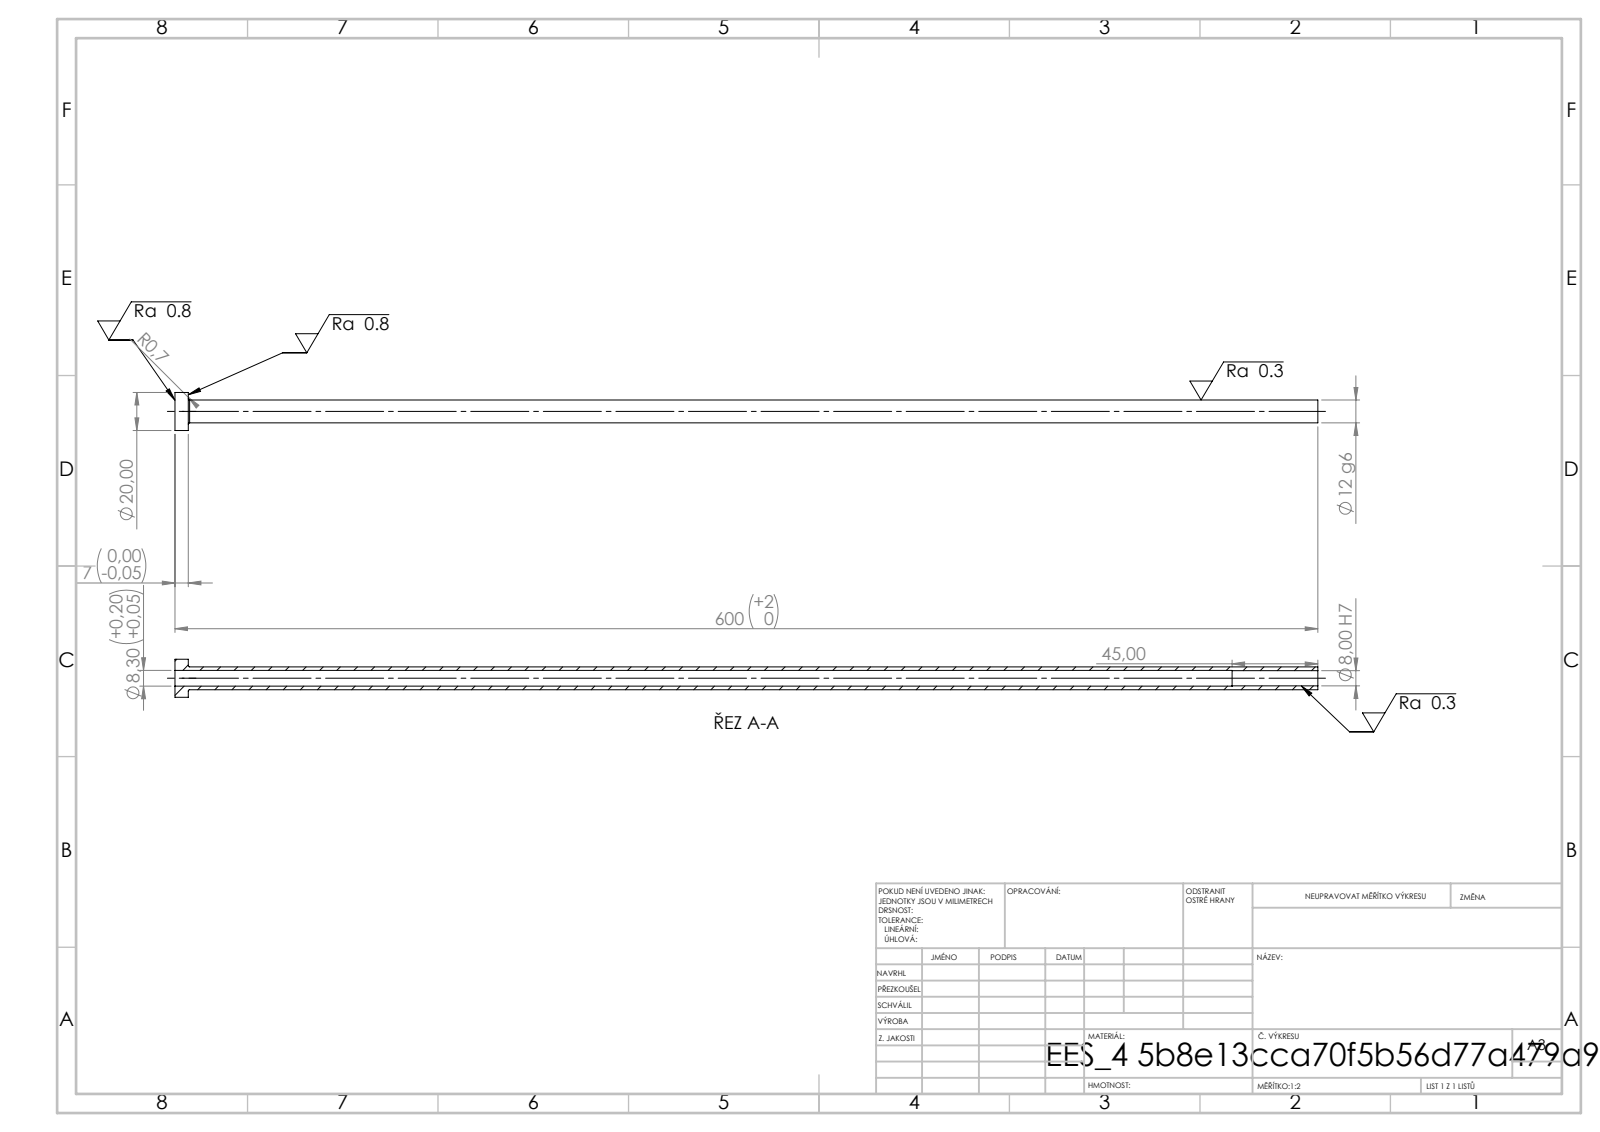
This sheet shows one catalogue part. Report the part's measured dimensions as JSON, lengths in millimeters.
{"step_written_by": "SolidWorks 2019 (CONFIG_CONTROL_DESIGN)", "units": "millimeters", "bodies": {"solids": 1, "faces": 14, "planar": 4, "cylindrical": 8, "other": 2}, "overall_size": [600, 20, 20], "volume_mm3": 36979, "surface_area_mm2": 38915, "round_holes": [[8, 1], [8.3, 1]], "round_bosses_or_shafts": [[20, 1], [12, 1]], "face_to_face_distances": [7, 600, 593, 555, 548, 45]}
